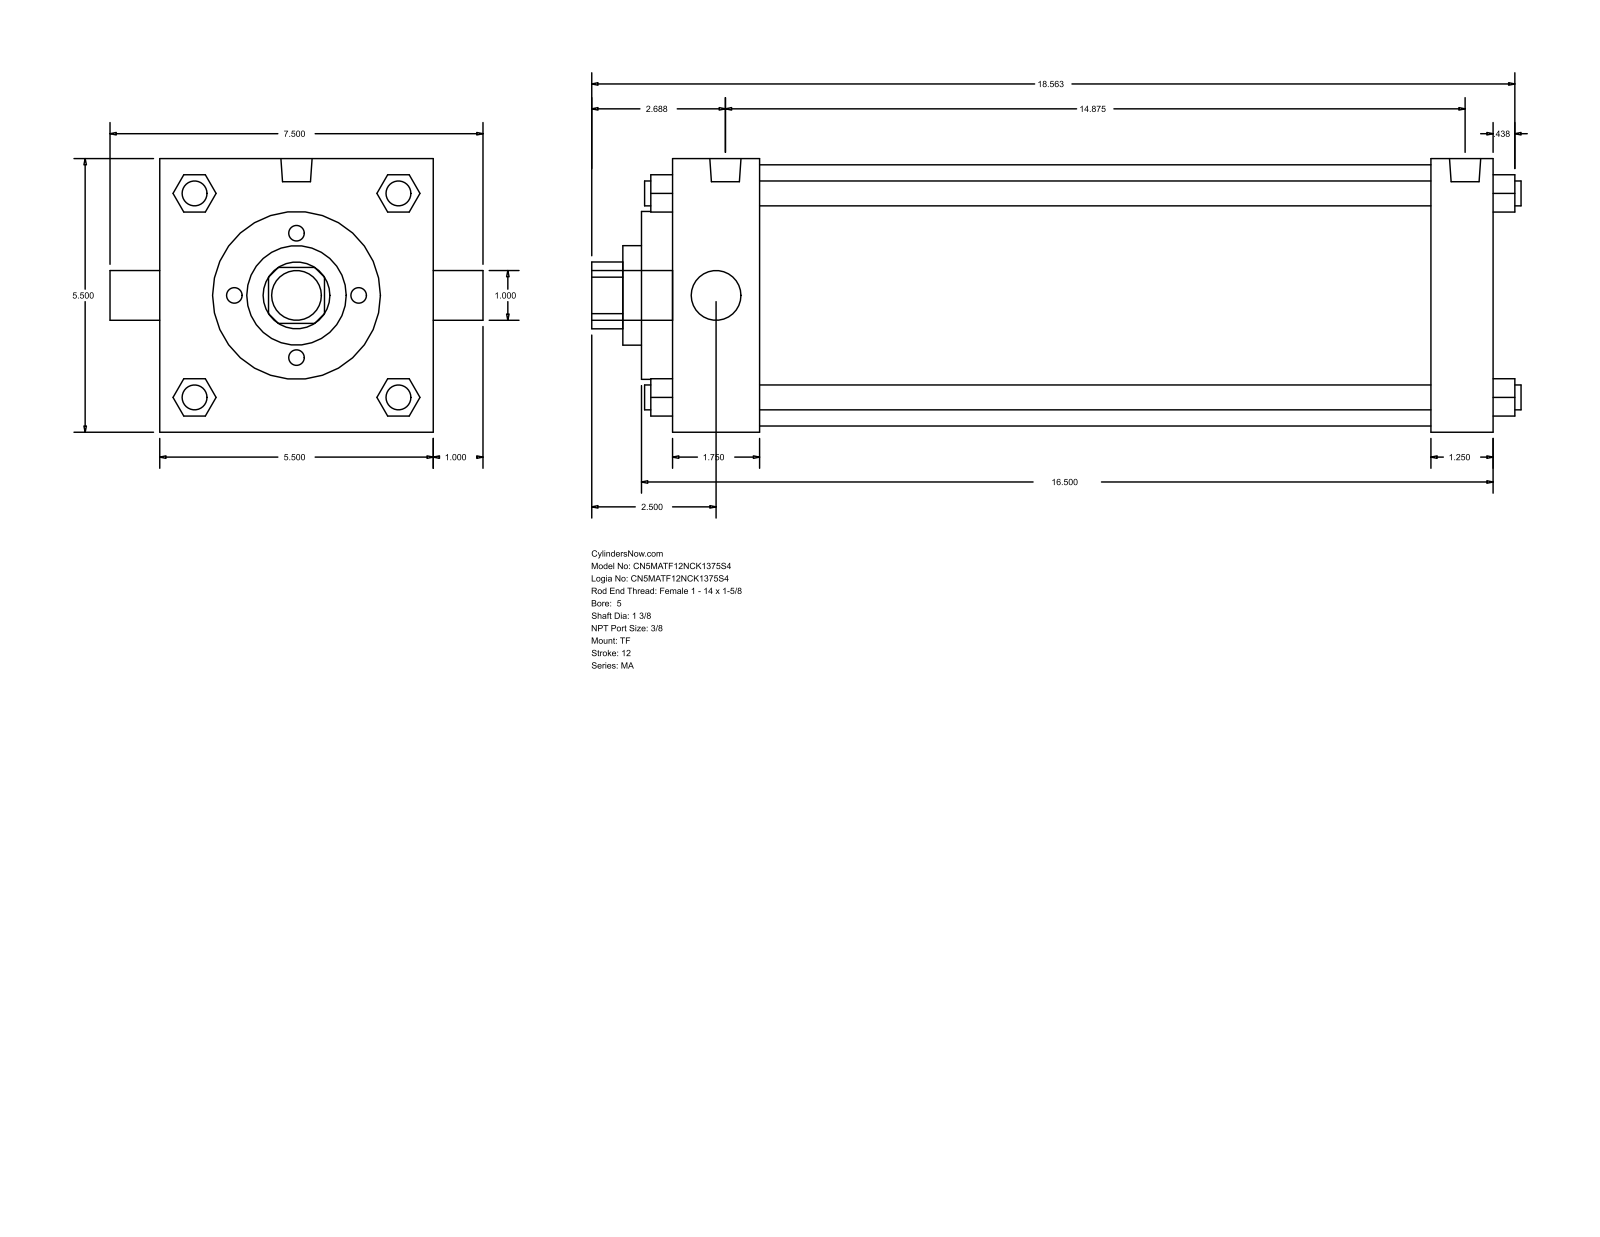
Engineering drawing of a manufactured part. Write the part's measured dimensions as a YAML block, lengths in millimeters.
part_name: "MA_TF__0500_1.375"
step_written_by: "GSSL Pune (CONFIG_CONTROL_DESIGN)"
units: millimeters
bodies: {solids: 0, faces: 122, planar: 93, cylindrical: 29, other: 0}
overall_size: [474.66, 190.5, 139.7]
round_holes:
  - {diameter: 25.4, count: 1}
  - {diameter: 34.92, count: 1}
  - {diameter: 50.8, count: 1}
  - {diameter: 85.72, count: 1}
  - {diameter: 133.35, count: 1}
round_bosses_or_shafts:
  - {diameter: 12.7, count: 4}
  - {diameter: 11.11, count: 3}
  - {diameter: 15.93, count: 2}
  - {diameter: 25.4, count: 1}
partial_cylinders:
  - {radius: 17.06, count: 1}
face_to_face_distances: [139.7, 419.11, 387.35, 31.76, 44.45, 342.9, 374.66, 15.87, 60.32, 403.22]
